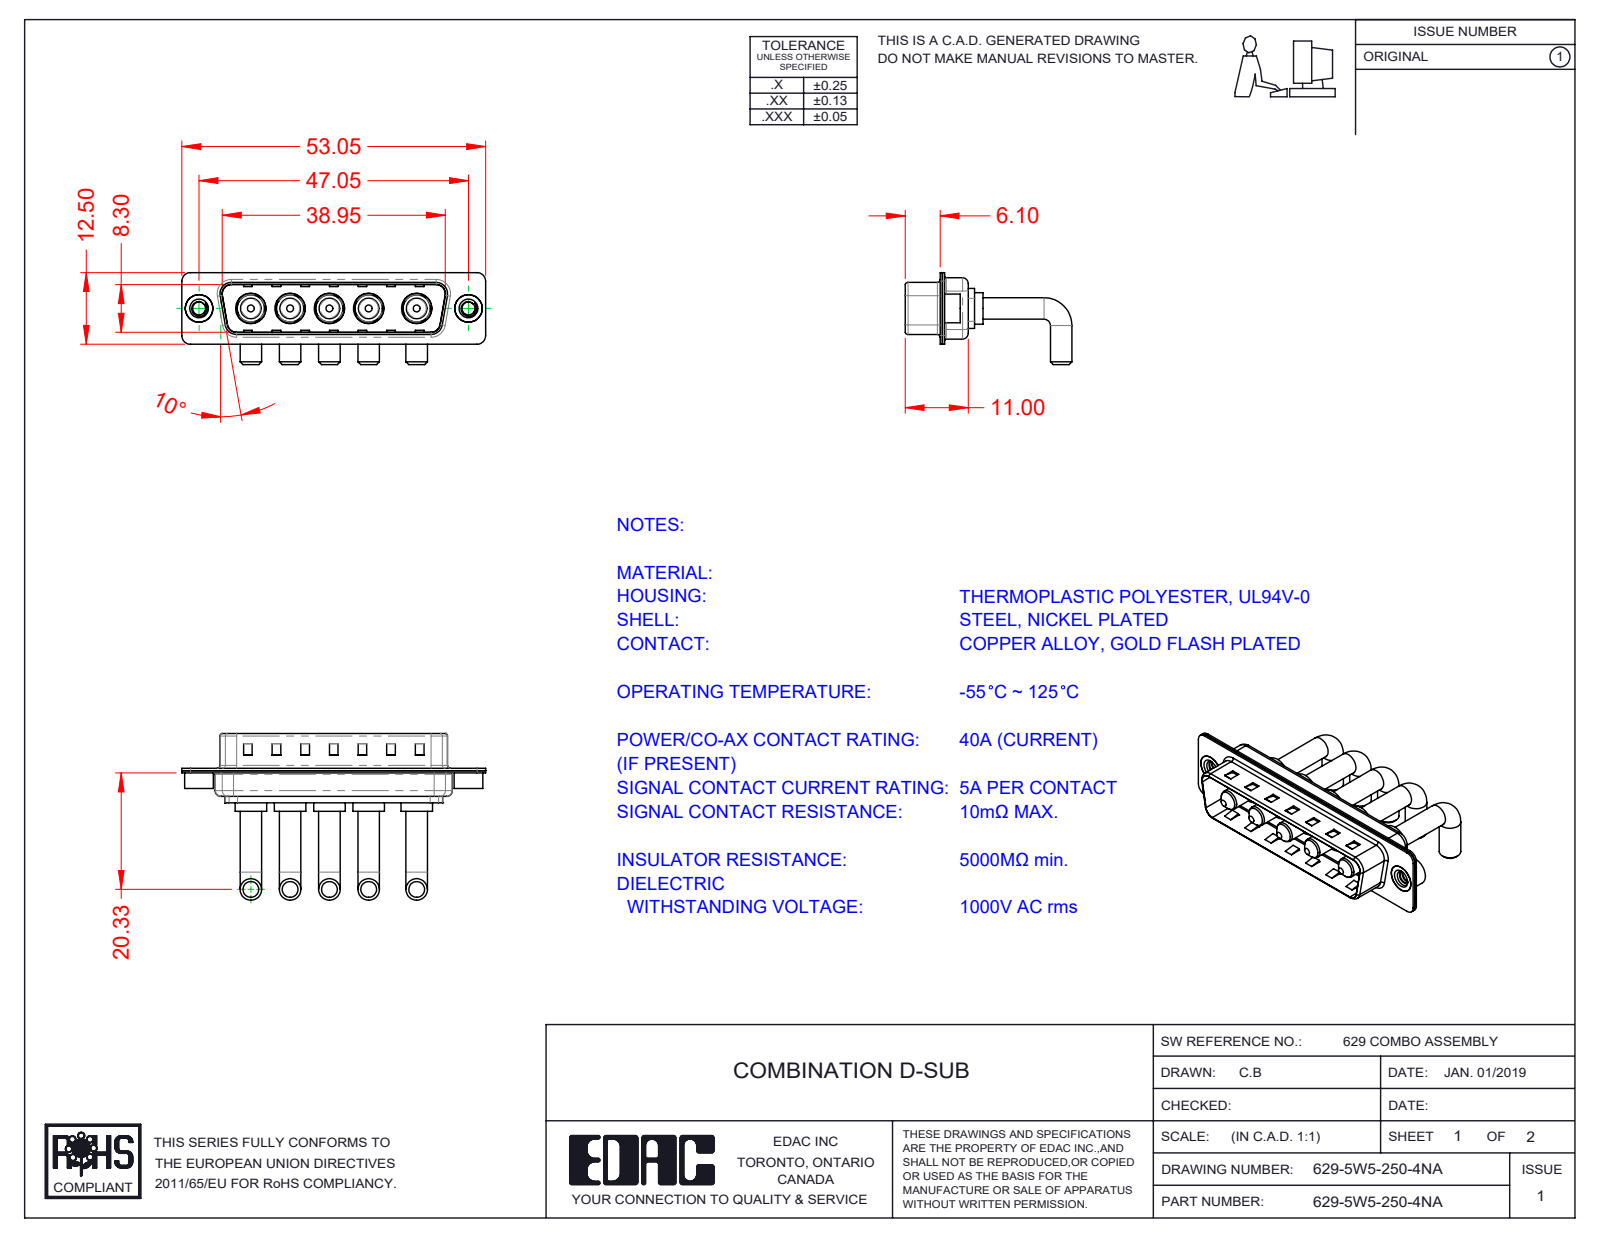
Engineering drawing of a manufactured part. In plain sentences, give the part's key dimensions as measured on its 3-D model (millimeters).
The part is named "Power Pin_Ext 40A RA; 629-5W5-250-4NA; 629Combo Threaded Rivet_2; 629Combo Shell Rear_25 Contacts (+2 more)". Its 3-D file was written by "SolidWorks 2020 (CONFIG_CONTROL_DESIGN)". It is 15 solids with 591 faces: 221 planar, 242 cylindrical and 128 other. Overall it measures 53.05 by 29.11 by 16.05 millimeters. Its volume is 4 161 cubic millimeters and its surface area 7 786 square millimeters. Round holes: 5 of diameter 4.85, 5 of diameter 5.3, 2 of diameter 2.26, 2 of diameter 4, 2 of diameter 4.8. Round bosses or shafts: 10 of diameter 3.75, 5 of diameter 5.5, 5 of diameter 5.2, 5 of diameter 4.75, 5 of diameter 3.6, 2 of diameter 5, 2 of diameter 4.9. Partial cylindrical surfaces (rounded edges, fillets, slot ends): 16 of radius 1.5, 12 of radius 2, 8 of radius 0.5, 8 of radius 1.6, 5 of radius 2.1, 4 of radius 0.25, 4 of radius 0.6, 4 of radius 0.65. The main face-to-face distances are 0.4, 0.8, 9.5, 9.1, 8.7, 9.9, 0.75, 1.2, 0.35, 6. The hole center spacings are 6.86, 13.73, 6.85, 6.87, 8.37, 8.38, 9.04, 9.05.
